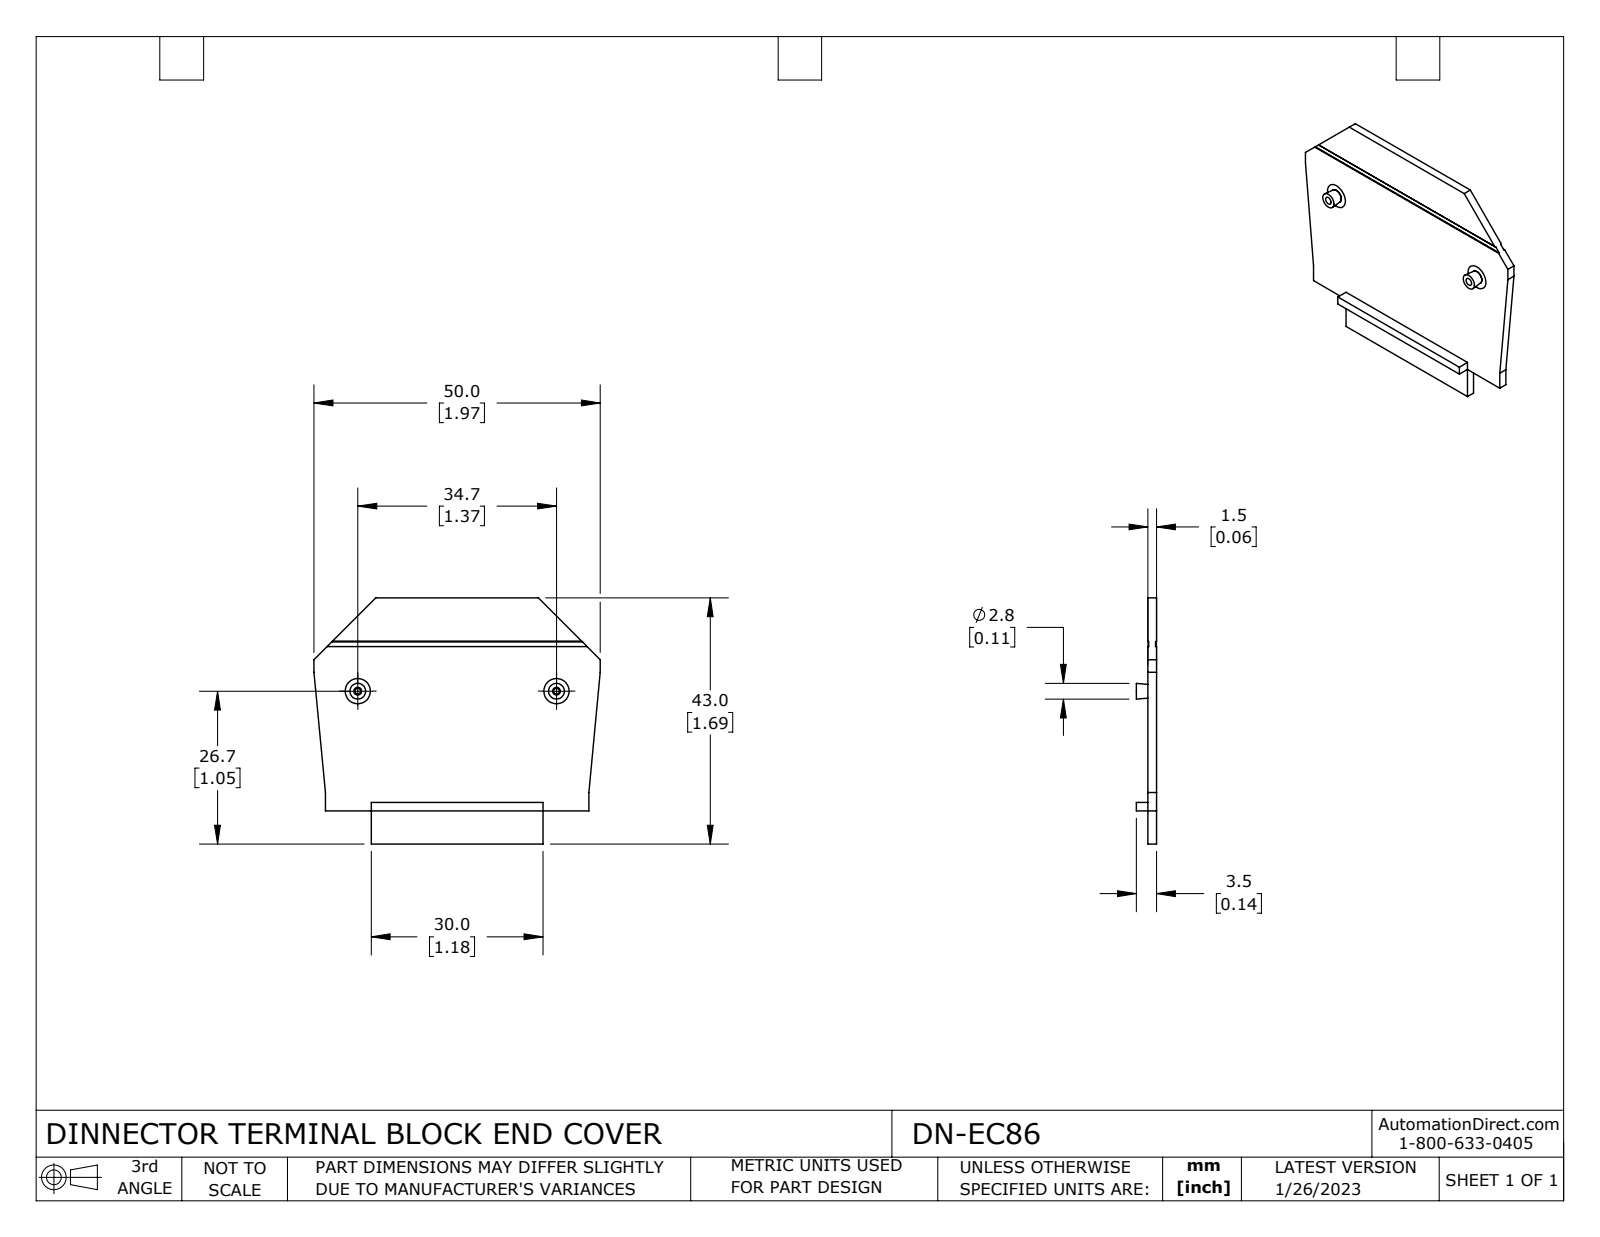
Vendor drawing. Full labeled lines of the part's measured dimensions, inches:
Part name (STEP PRODUCT): DN-EC86
STEP written by: SolidWorks 2021 (CONFIG_CONTROL_DESIGN)
Units: inches
Bodies: 1 solid, 50 faces (34 planar, 0 cylindrical, 16 other)
Overall size (bounding box): 1.969 × 1.693 × 0.138
Volume: 0.176 in³ · Surface area: 6.489 in²
Main face-to-face distances: 0.059, 0.053, 0.079, 0.138, 0.228, 0.287, 1.693, 1.465, 1.406, 0.132
